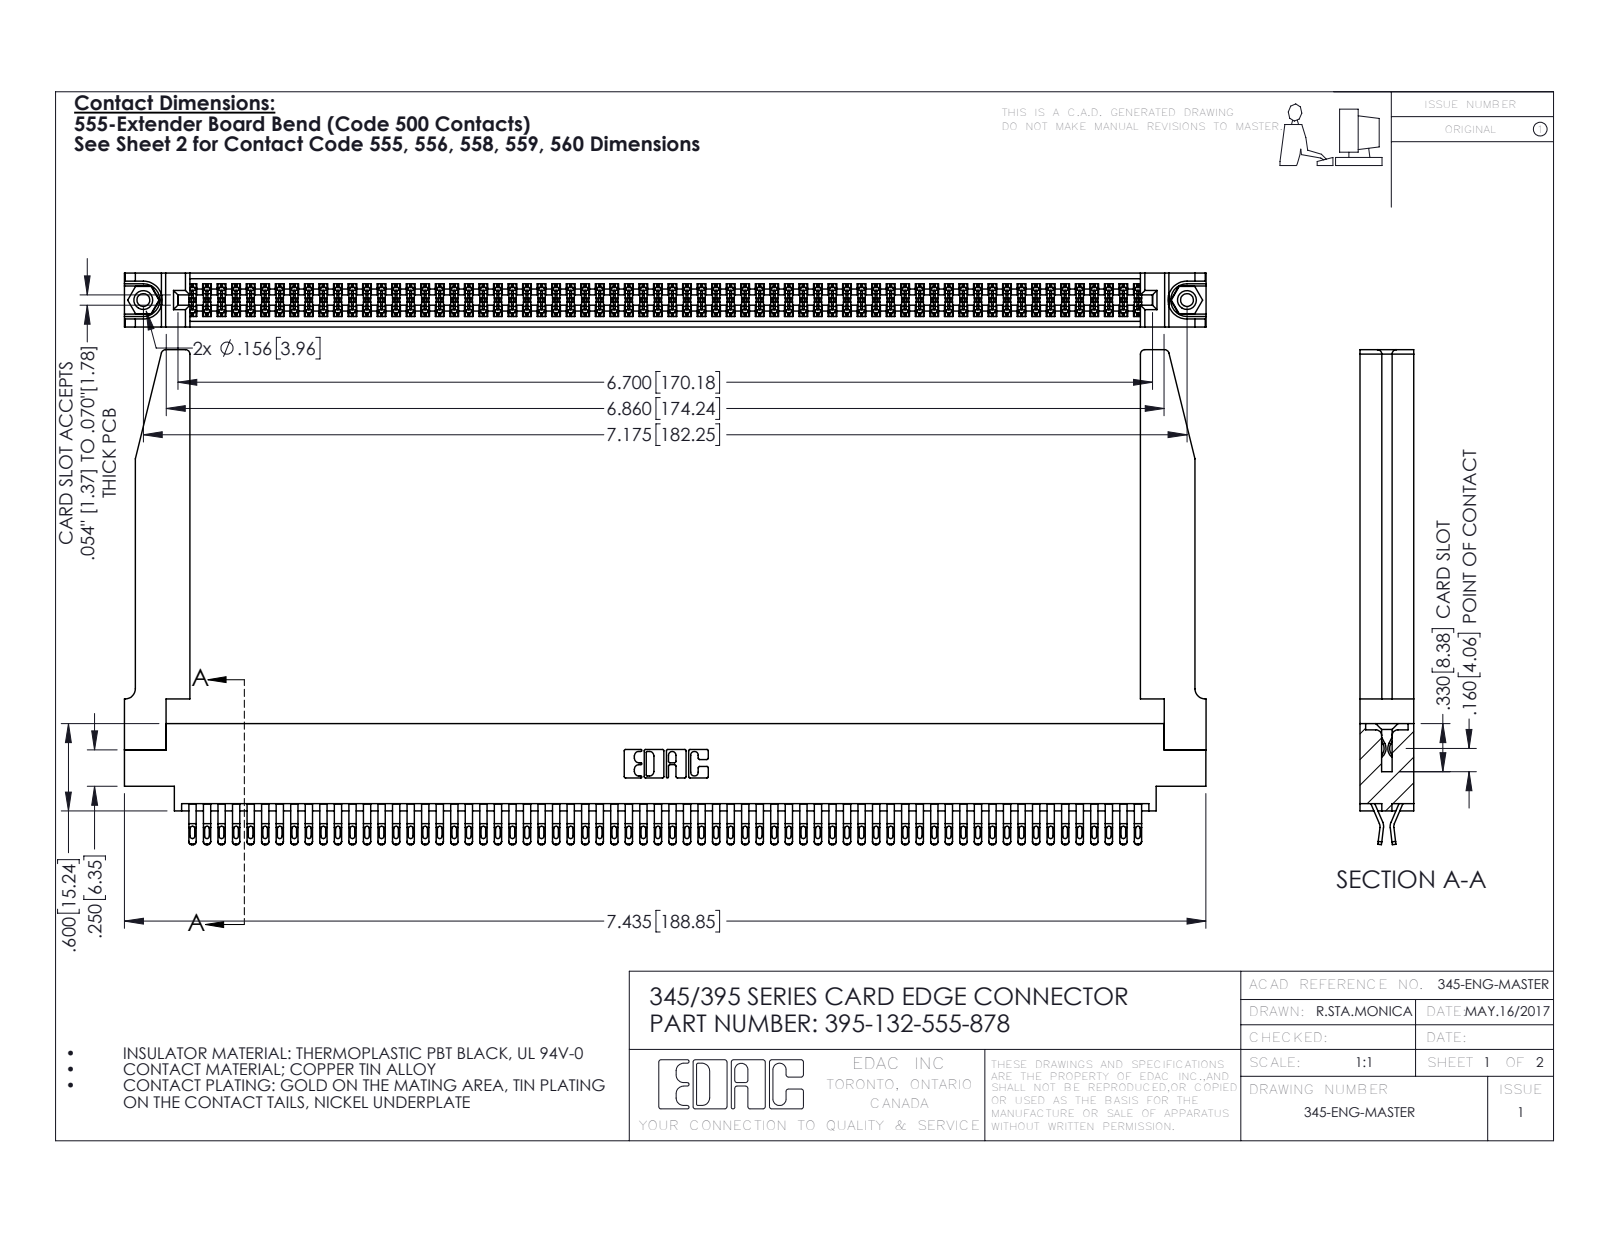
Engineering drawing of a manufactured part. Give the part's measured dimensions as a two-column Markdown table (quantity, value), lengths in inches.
| quantity | value |
| --- | --- |
| part name | 345 Part_0.170 Offset - 0.156 Dia-TH; 345-250-001_345-250-001-102; 395-132-555-878; 345-292-001_555 Tail (+1 more) |
| STEP written by | SolidWorks 2016 (CONFIG_CONTROL_DESIGN) |
| units | inches |
| bodies | 137 solids, 7756 faces (4318 planar, 3386 cylindrical, 52 other) |
| overall size | 7.436 × 3.402 × 0.37 |
| volume | 1.624 in³ |
| surface area | 56.77 in² |
| round holes (diameter × count) | 0.089 × 2, 0.125 × 2, 0.156 × 2, 0.064 × 1 |
| round bosses / shafts (diameter × count) | 0.155 × 2 |
| partial cylindrical surfaces (radius × count) | 0.016 × 330, 0.02 × 264, 0.006 × 198, 0.01 × 22, 0.03 × 8, 0.007 × 6, 0.031 × 6, 0.026 × 3 |
| main face-to-face distances | 0.072, 0.37, 0.298, 0.025, 0.098, 0.272, 0.2, 0.225, 0.175, 0.15 |
| hole center spacings | 0.27, 6.939, 7.175 |
